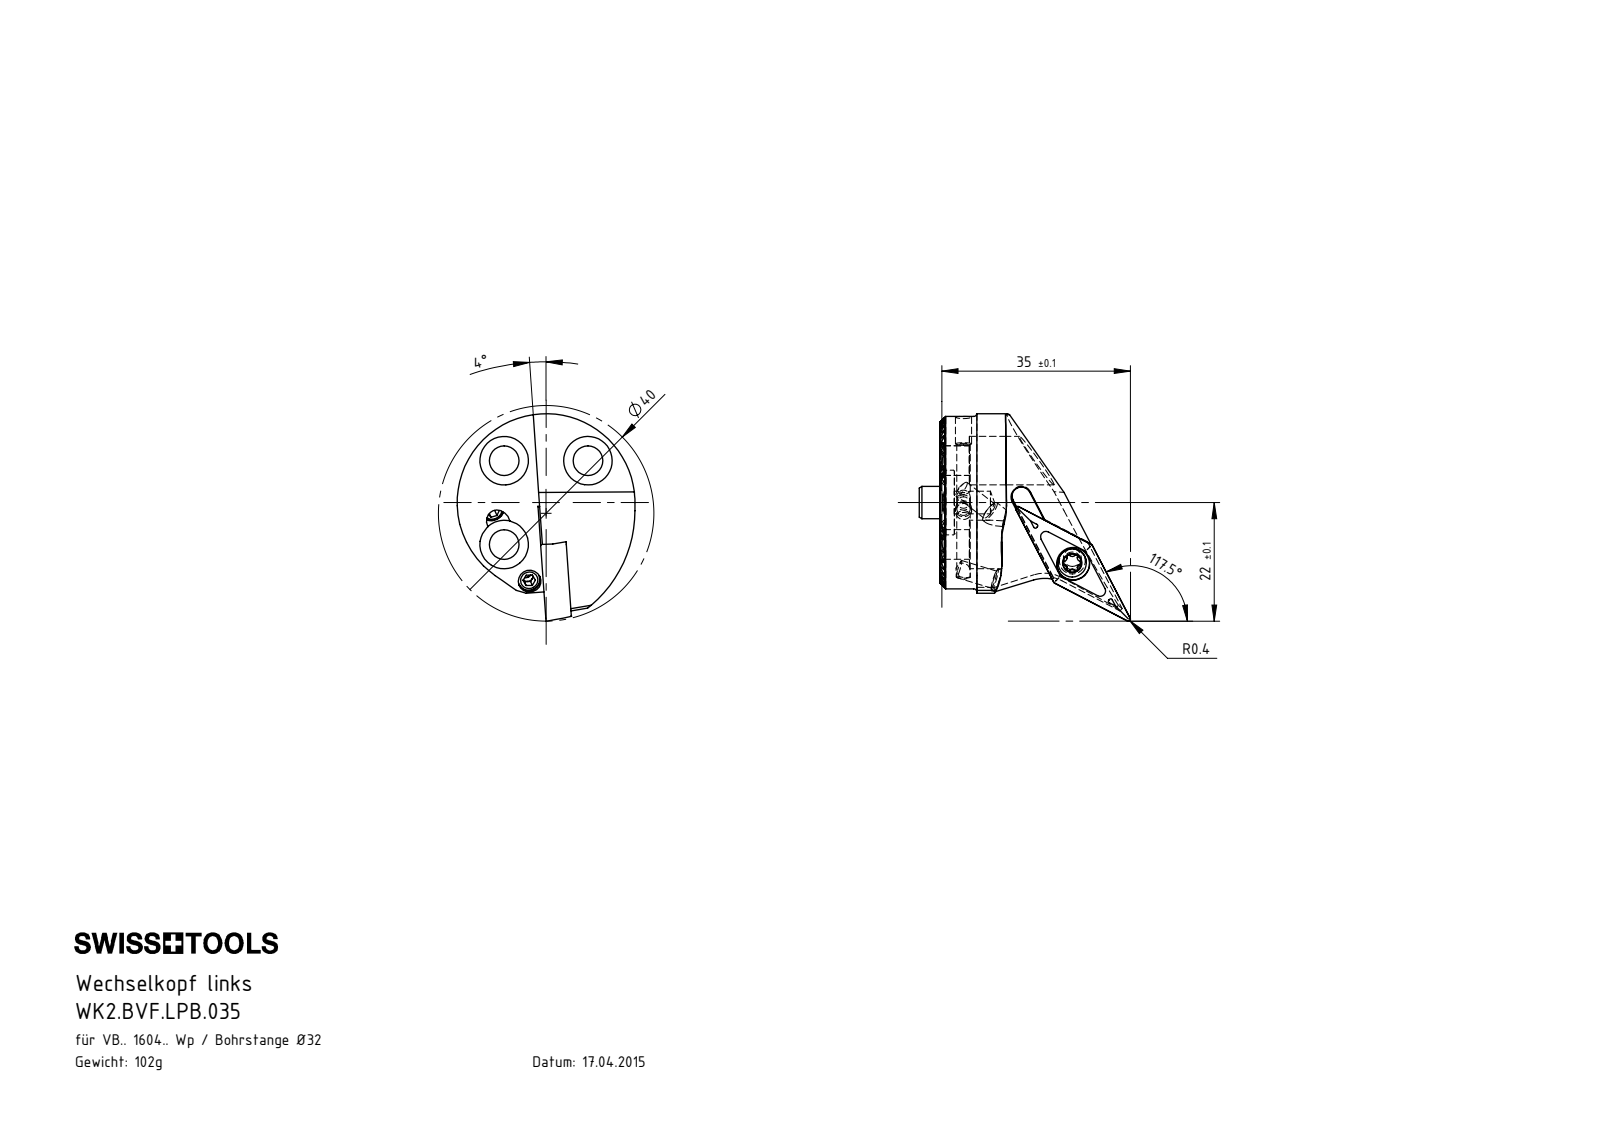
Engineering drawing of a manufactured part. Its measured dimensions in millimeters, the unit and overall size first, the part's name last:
Units: millimetres
Overall size (bounding box): 39.2 × 38.5 × 33
Round holes (diameter × count): ⌀3.3 ×3, ⌀4.2 ×3, ⌀5.5 ×3, ⌀9 ×3, ⌀1.7 ×2, ⌀2.38 ×2, ⌀2.5 ×2, ⌀3 ×2, ⌀4.4 ×1, ⌀6.1 ×1, ⌀12 ×1
Round bosses / shafts (diameter × count): ⌀4 ×3, ⌀3 ×2, ⌀32 ×1, ⌀6 ×1, ⌀5.25 ×1
Partial cylindrical surfaces — rounded edges, fillets, slot ends (radius × count): R0.12 ×22, R0.34 ×6, R0.59 ×6, R12 ×3, R0.15 ×2, R1.75 ×1, R7 ×1, R16.5 ×1
Main face-to-face distances: 1.3, 2.6, 3.9, 5.2, 6.5, 12.99, 11.69, 14.29, 7.8, 10.39
Hole centre spacings: 11, 15.56, 22.01
Volume: 12 380 mm³ · Surface area: 7 498 mm²
Bodies: 10 solids, 531 faces (198 planar, 185 cylindrical, 148 other)
Part name (STEP PRODUCT): WK2.BVF.LPB.035; VBMT160404; WK2-ER1.001.012_A_Fertigbearbeitung; WKX-ER1.004.005_A_PreviewCfg (+3 more)
STEP written by: SolidWorks 2017 (AUTOMOTIVE_DESIGN)
